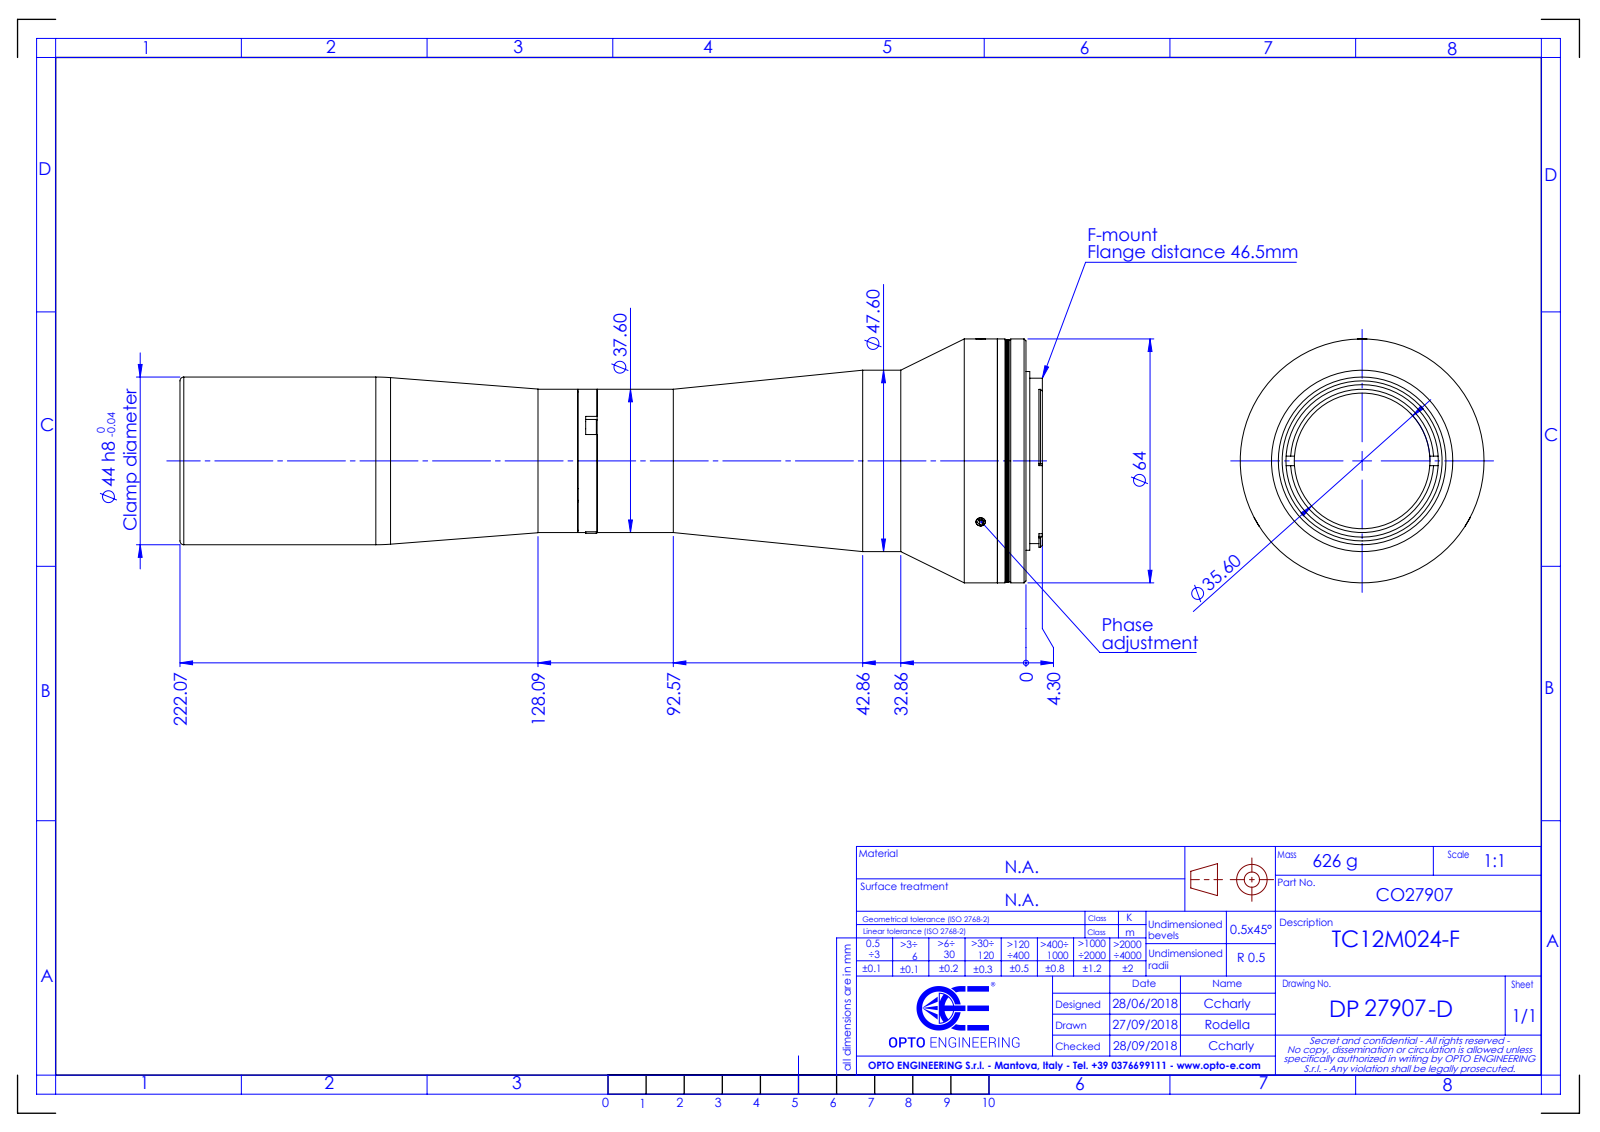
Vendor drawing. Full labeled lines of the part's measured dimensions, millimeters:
Part name (STEP PRODUCT): DP27907_TC12M024-F
STEP written by: SolidWorks 2021 (CONFIG_CONTROL_DESIGN)
Units: millimetres
Bodies: 0 solids, 159 faces (66 planar, 57 cylindrical, 36 other)
Overall size (bounding box): 226.37 × 64 × 64
Round holes (diameter × count): ⌀35.6 ×1, ⌀40 ×1, ⌀42 ×1
Round bosses / shafts (diameter × count): ⌀5.5 ×3, ⌀64 ×1, ⌀63.5 ×1, ⌀47.6 ×1, ⌀46.9 ×1, ⌀44 ×1, ⌀43.4 ×1, ⌀37.6 ×1
Partial cylindrical surfaces — rounded edges, fillets, slot ends (radius × count): R0.5 ×6, R1.15 ×2, R22.65 ×1
Main face-to-face distances: 5.3, 5.1, 2.2, 2.4, 7.5, 2, 5.5, 105.07, 107.27, 107.47
